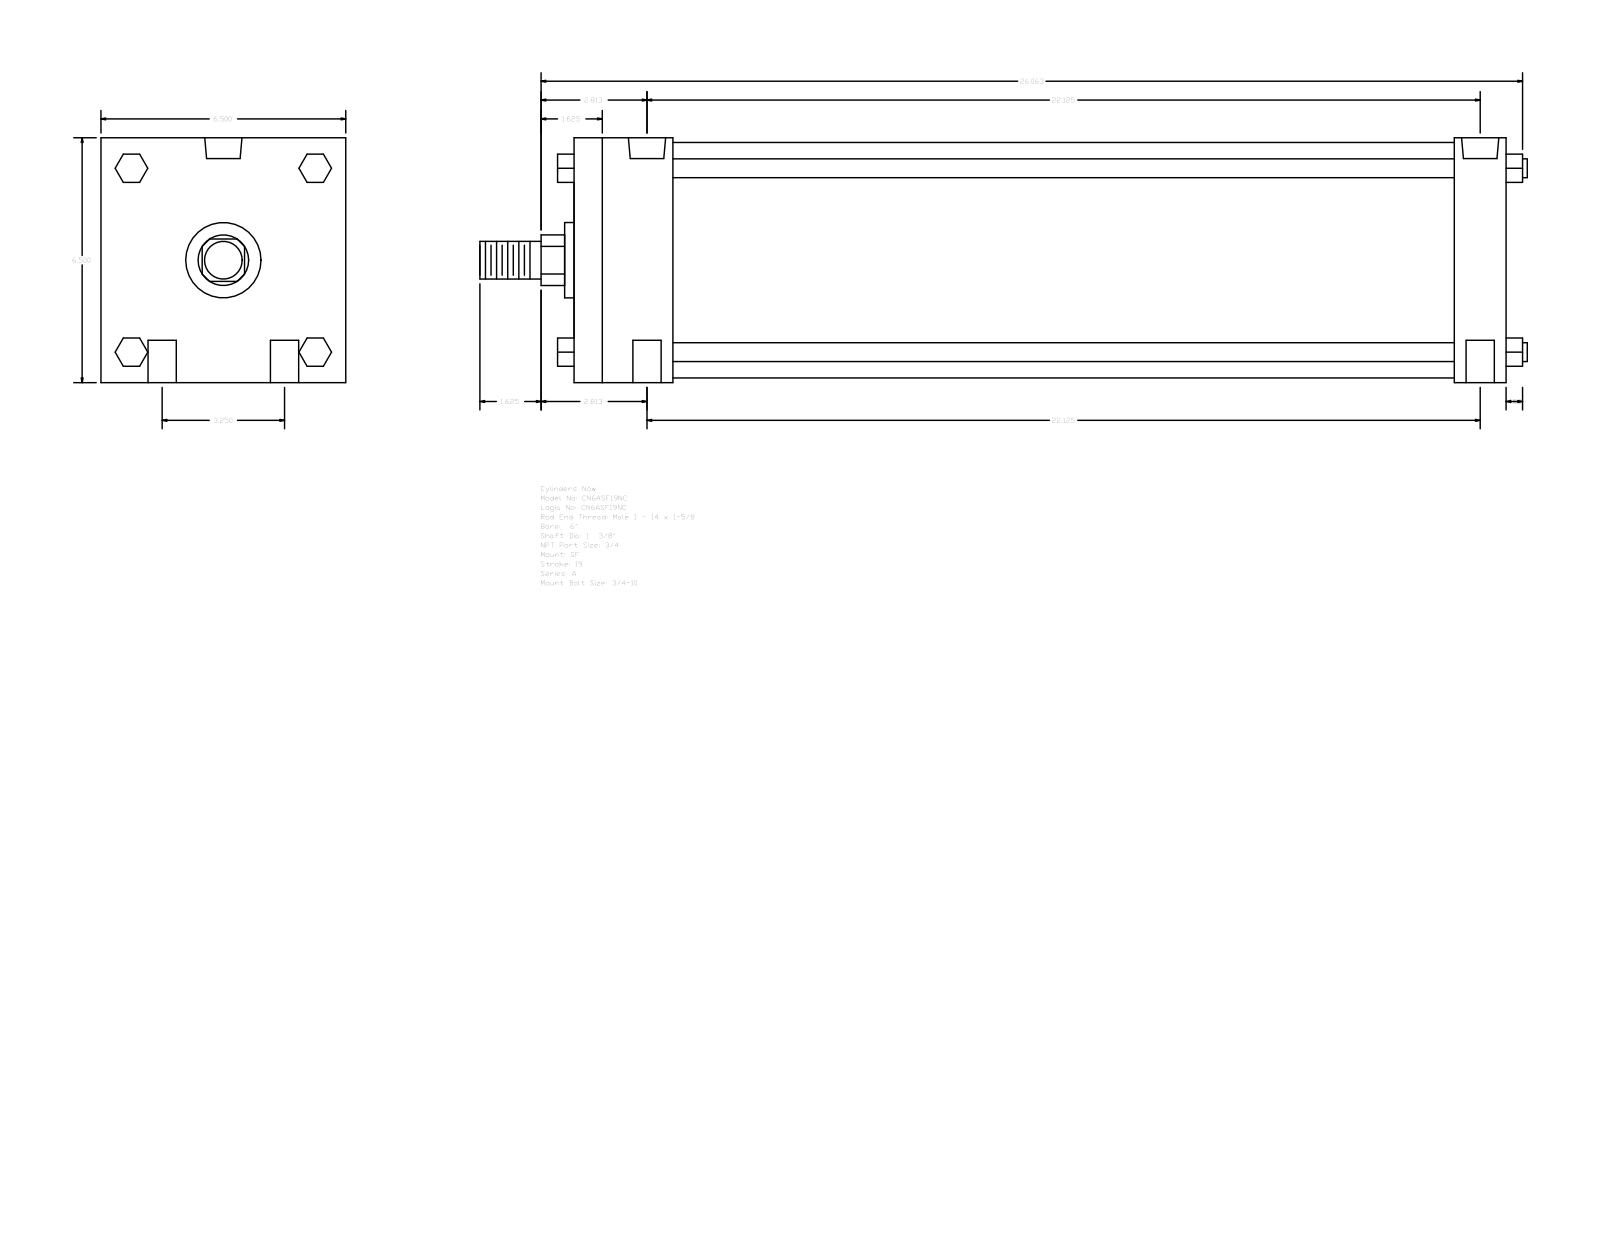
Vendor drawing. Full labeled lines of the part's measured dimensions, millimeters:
Part name (STEP PRODUCT): A_SF__0600_1.375
STEP written by: GSSL Pune (CONFIG_CONTROL_DESIGN)
Units: millimetres
Bodies: 0 solids, 124 faces (94 planar, 30 cylindrical, 0 other)
Overall size (bounding box): 706.44 × 165.1 × 165.1
Round holes (diameter × count): ⌀19.05 ×4, ⌀15.08 ×2, ⌀25.12 ×2
Round bosses / shafts (diameter × count): ⌀12.7 ×4, ⌀158.75 ×1, ⌀50.8 ×1, ⌀34.92 ×1, ⌀25.4 ×1
Partial cylindrical surfaces — rounded edges, fillets, slot ends (radius × count): R17.06 ×1
Main face-to-face distances: 165.1, 628.65, 593.72, 34.93, 66.67, 527.05, 561.98, 19.05, 61.97, 107.34
Hole centre spacings: 41.27, 563.48, 561.97, 82.54, 568, 550.85
